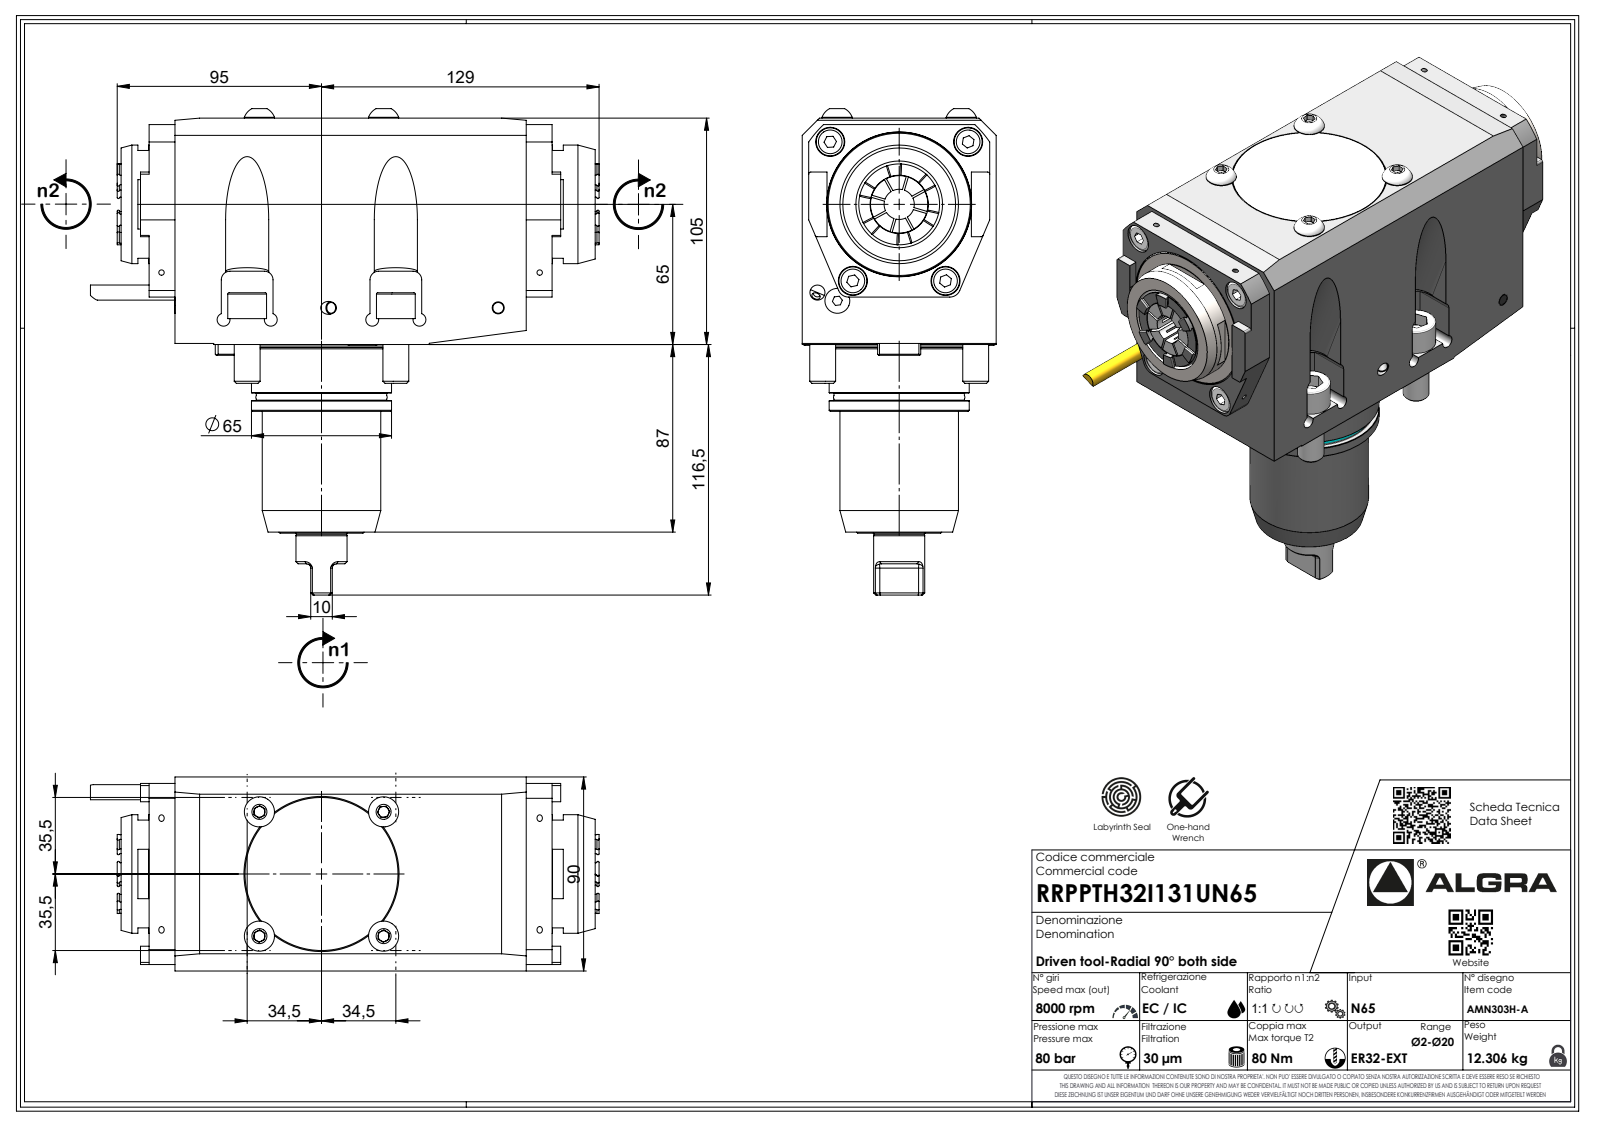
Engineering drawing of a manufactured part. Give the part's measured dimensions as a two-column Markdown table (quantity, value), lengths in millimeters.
| quantity | value |
| --- | --- |
| part name | RRPPTH32I131UN65 |
| STEP written by | SolidWorks 2023 (AUTOMOTIVE_DESIGN) |
| units | millimeters |
| bodies | 1 solid, 505 faces (319 planar, 76 cylindrical, 110 other) |
| overall size | 230 × 221.2 × 90 |
| volume | 2 010 000 mm³ |
| surface area | 117 626 mm² |
| round holes (diameter × count) | 2.1 × 1 |
| round bosses / shafts (diameter × count) | 12 × 4, 55 × 2, 65 × 1, 64.6 × 1, 60.5 × 1, 23.7 × 1, 6.37 × 1, 1.7 × 1 |
| partial cylindrical surfaces (radius × count) | 3 × 8, 0.33 × 7, 0.52 × 7, 3.7 × 7, 2 × 6, 1 × 4, 5 × 2, 0.21 × 1 |
| main face-to-face distances | 90, 12, 175, 105, 3, 187, 87, 163, 0.5, 18 |
